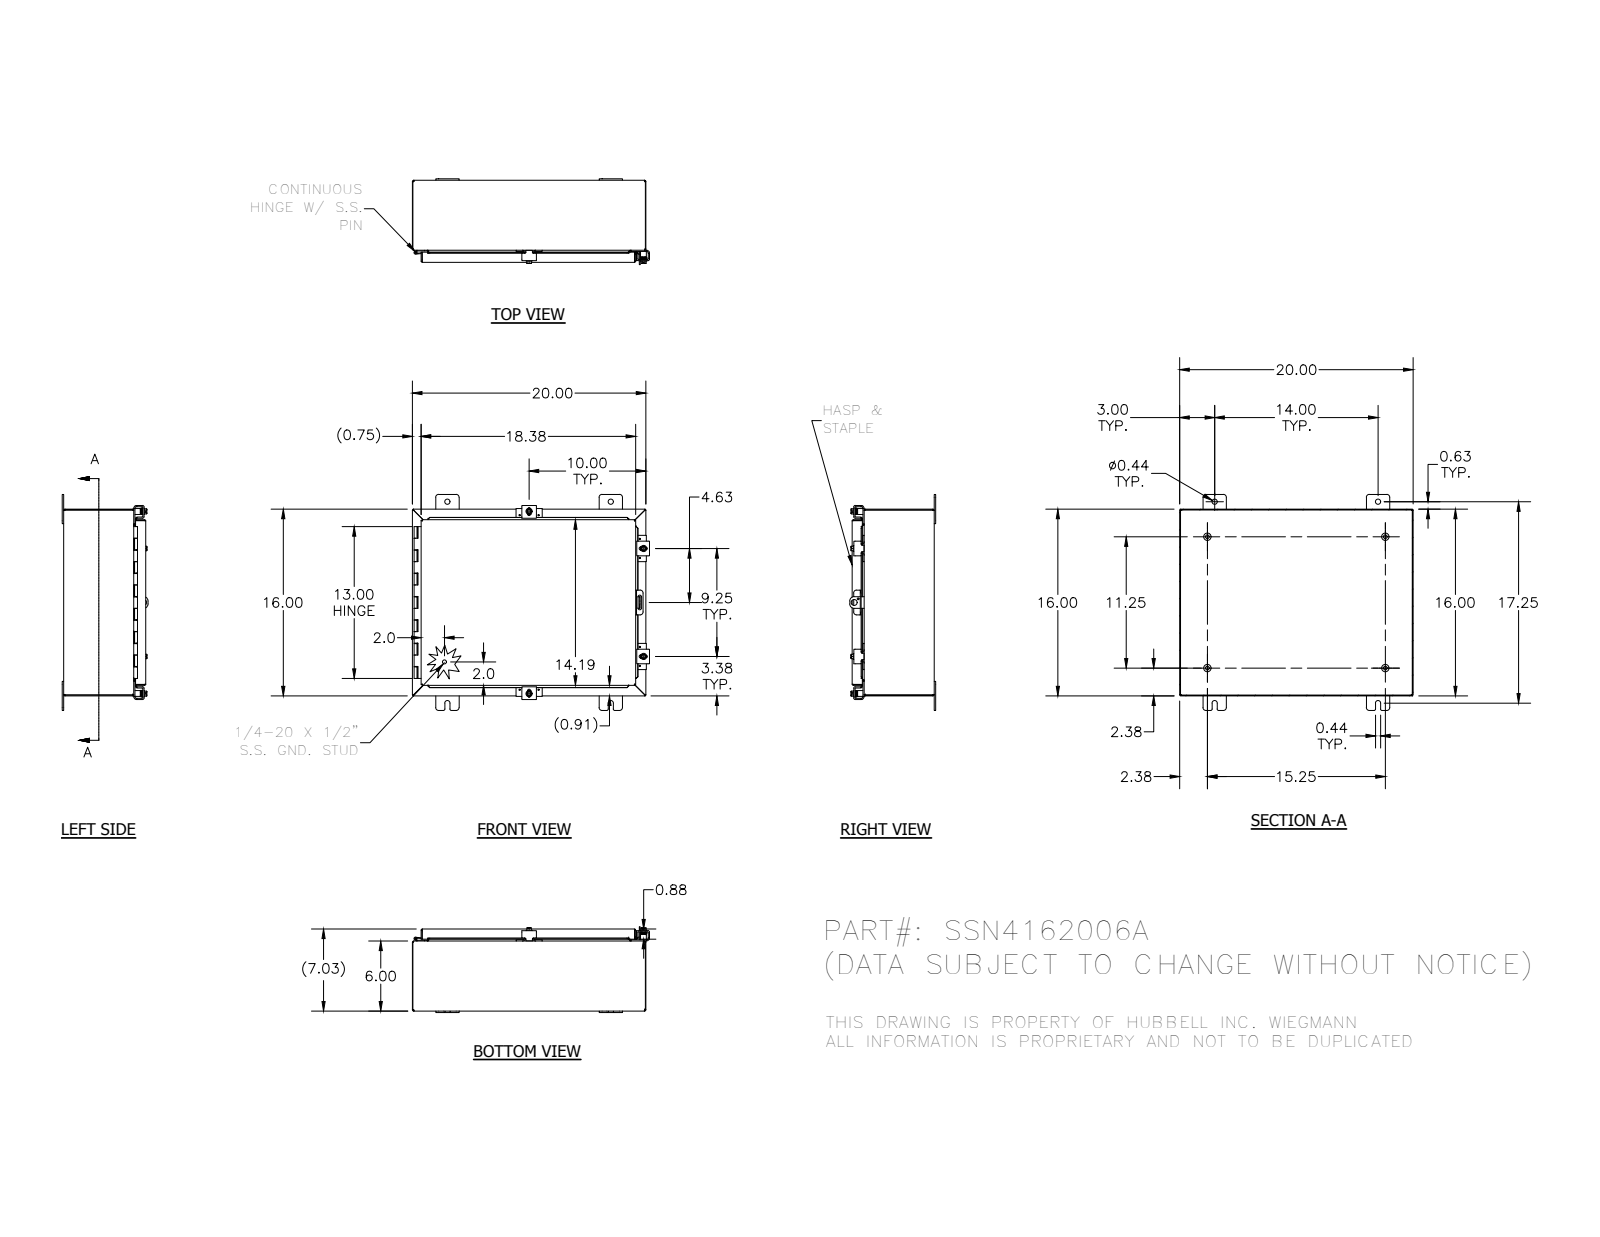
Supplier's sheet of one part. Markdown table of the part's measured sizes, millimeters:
| quantity | value |
| --- | --- |
| part name | 32874-16P; 30824-2; 32874-16L; 30818 (+8 more) |
| STEP written by | SolidWorks 2014 (AUTOMOTIVE_DESIGN) |
| units | millimeters |
| bodies | 37 solids, 1384 faces (551 planar, 592 cylindrical, 241 other) |
| overall size | 513.5 × 469.9 × 186.8 |
| volume | 1 691 000 mm³ |
| surface area | 1 729 000 mm² |
| round holes (diameter × count) | 2.8 × 8, 5.4 × 4, 7.1 × 4, 7.6 × 4, 11.1 × 4, 3.2 × 1, 4 × 1, 12.7 × 1 |
| round bosses / shafts (diameter × count) | 6.4 × 6, 15.9 × 4, 13.2 × 4, 12.7 × 4, 8.9 × 4, 8.4 × 4, 8.6 × 1, 3 × 1 |
| partial cylindrical surfaces (radius × count) | 0.8 × 49, 3.2 × 33, 6.4 × 29, 0.8 × 23, 2.7 × 23, 1.6 × 14, 1.8 × 8, 3.6 × 8 |
| main face-to-face distances | 1.9, 176.8, 174.9, 178.6, 404.5, 506.1, 150.5, 26.2, 406.4, 402.6 |
| hole center spacings | 22.3, 388.9, 235, 22.3, 41.3, 41.3, 157.2, 159.8 |
